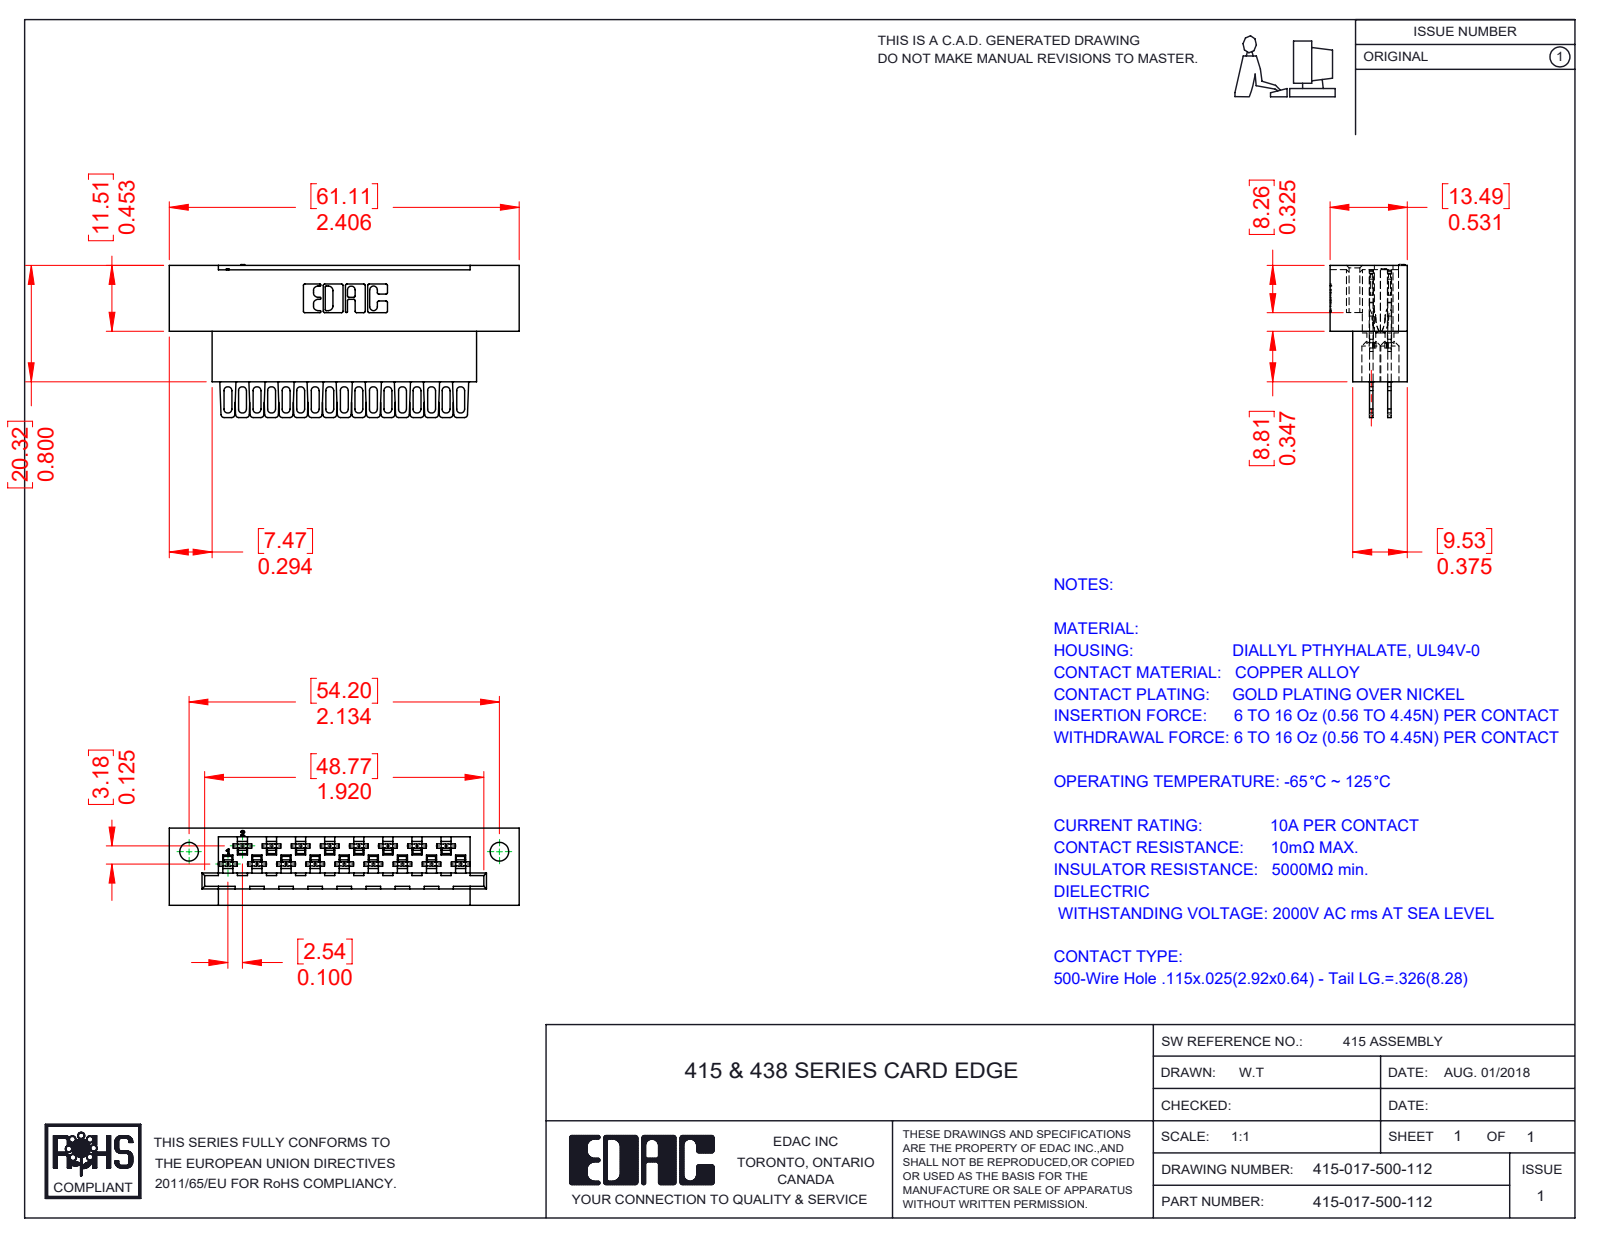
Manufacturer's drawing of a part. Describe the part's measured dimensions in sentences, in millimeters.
The part is named "415-017-500-112; 516-290-001_500; 415-210-001_415-210-017-112". Its 3-D file was written by "SolidWorks 2016 (CONFIG_CONTROL_DESIGN)". It is 18 solids with 1878 faces: 1166 planar, 537 cylindrical and 175 other. Overall it measures 61.11 by 26.68 by 13.49 millimeters. Its volume is 10 199 cubic millimeters and its surface area 11 978 square millimeters. Round holes: 17 of diameter 1.27, 17 of diameter 3.3, 2 of diameter 3.25. Partial cylindrical surfaces (rounded edges, fillets, slot ends): 68 of radius 0.3, 68 of radius 0.56, 34 of radius 0.18, 34 of radius 0.2, 34 of radius 0.41, 34 of radius 0.51, 34 of radius 0.69, 34 of radius 2.03. The main face-to-face distances are 3.18, 0.61, 13.49, 1.88, 7.49, 1.27, 20.32, 5.08, 6.61, 6.88. The hole center spacings are 5.08, 10.16, 15.24, 20.32, 2.54, 4.06, 7.62, 8.25.
